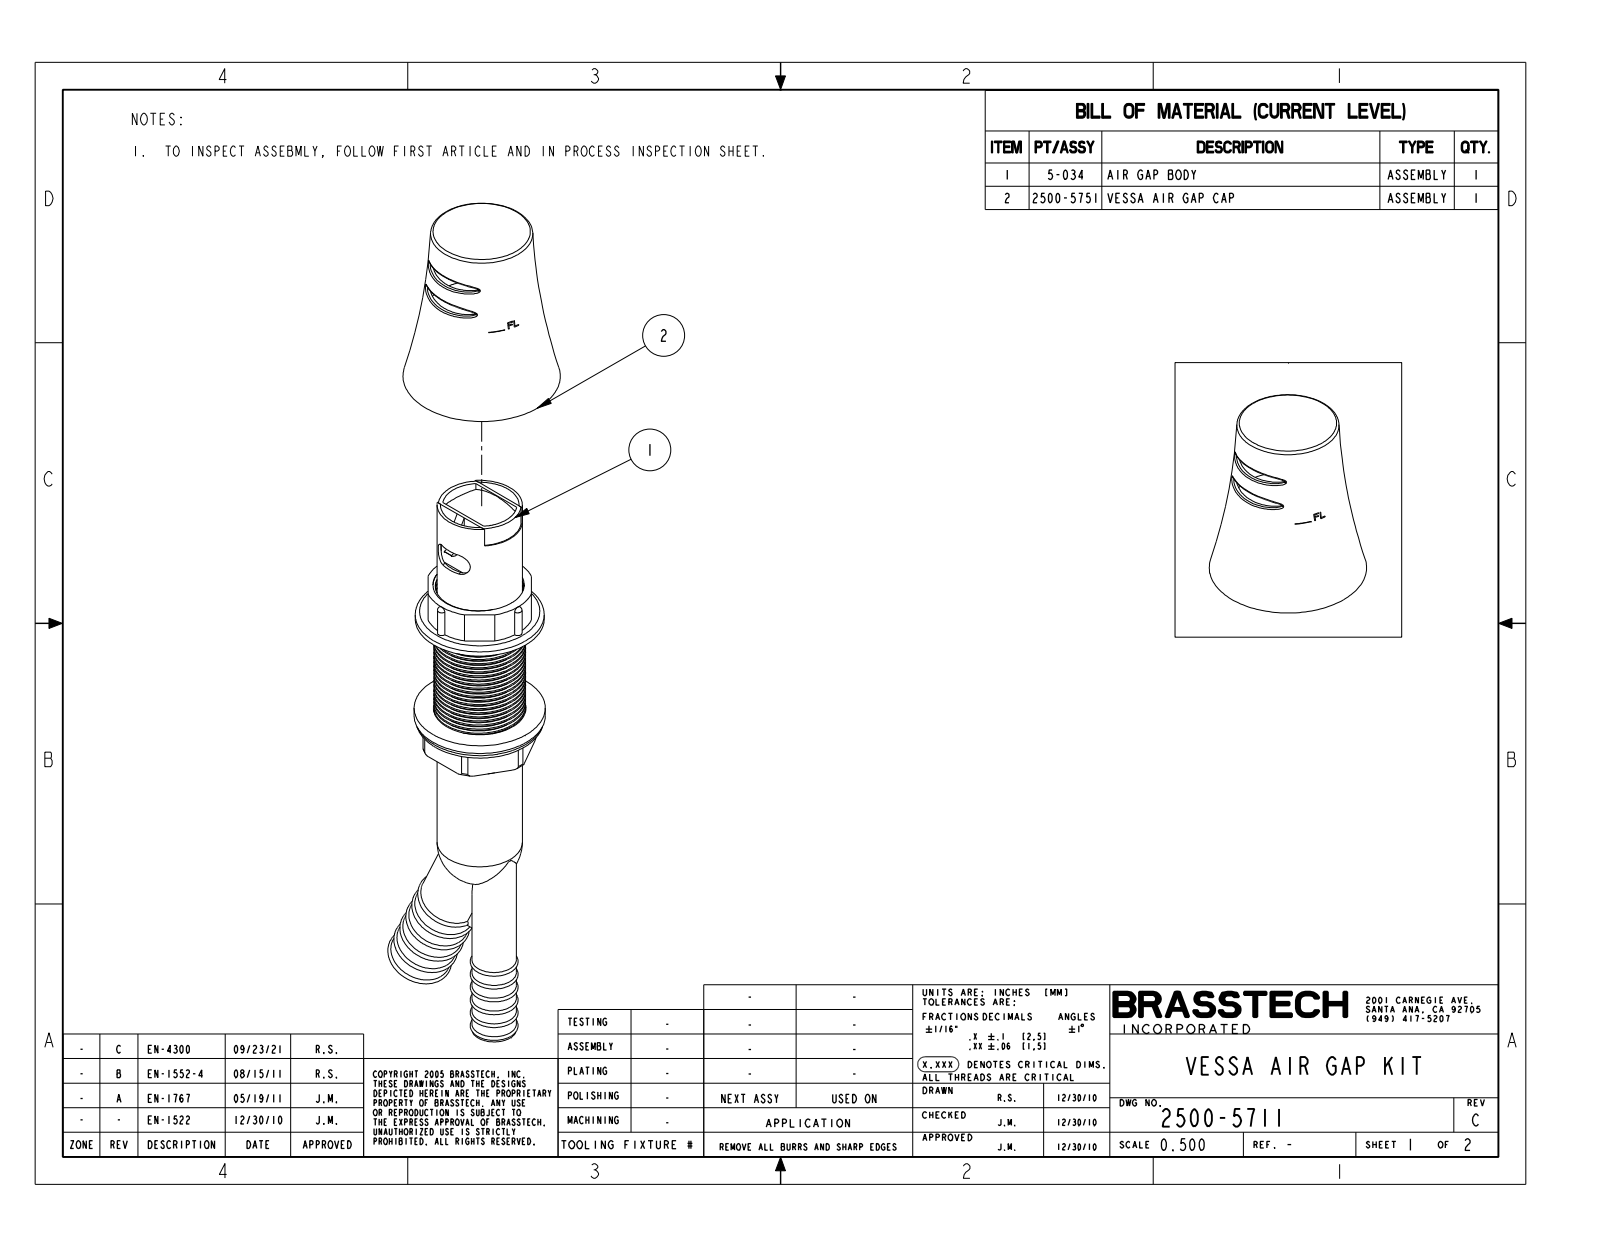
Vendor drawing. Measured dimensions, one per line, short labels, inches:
name: 2500-5711
written by: CREO PARAMETRIC BY PTC INC, 2018400 (AUTOMOTIVE_DESIGN)
unit: in
bodies: 1 solid, 261 faces (58 planar, 122 cylindrical, 81 other)
size: 9.258 × 2.662 × 2.16
volume: 11.37 in³; area: 72.1 in²
holes: 1× ⌀1.2, 1× ⌀1.27, 1× ⌀1.28
bosses: 1× ⌀1.8, 1× ⌀1.76, 1× ⌀1.259, 1× ⌀1.17, 1× ⌀0.854, 1× ⌀0.61
rounds: 6× R0.04, 2× R0.157
face distances: 1.5, 2.58, 1.08, 3.14, 1.64, 0.56, 1.42, 0.345, 1.075, 0.61
